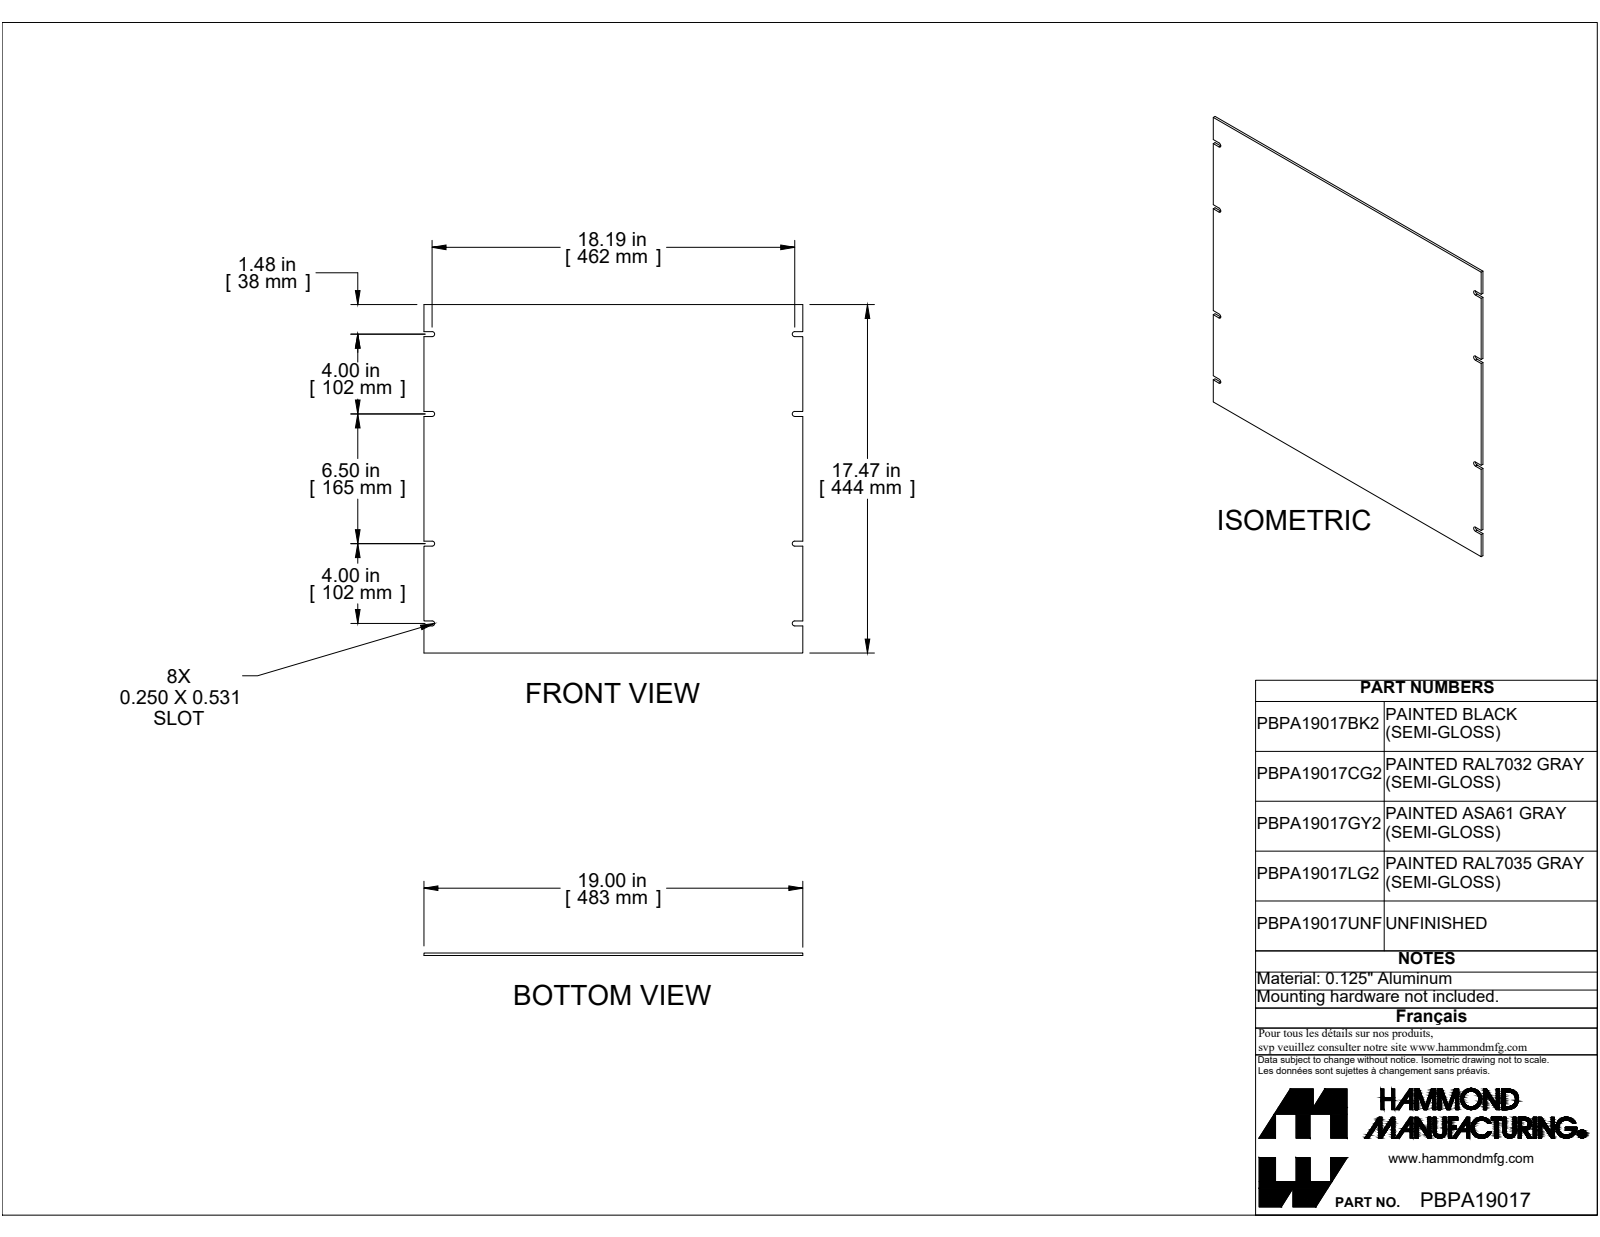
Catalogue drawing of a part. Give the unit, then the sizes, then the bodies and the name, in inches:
Units: inches
Overall size (bounding box): 19 × 17.468 × 0.125
Partial cylindrical surfaces — rounded edges, fillets, slot ends (radius × count): R0.125 ×8
Main face-to-face distances: 0.125, 17.468, 19, 1.359, 1.609, 5.359, 5.609, 11.859, 12.109, 15.859
Volume: 41.36 in³ · Surface area: 671.8 in²
Bodies: 1 solid, 38 faces (30 planar, 8 cylindrical, 0 other)
Part name (STEP PRODUCT): PBPA19017BK2
STEP written by: SolidWorks 2019 (CONFIG_CONTROL_DESIGN)
